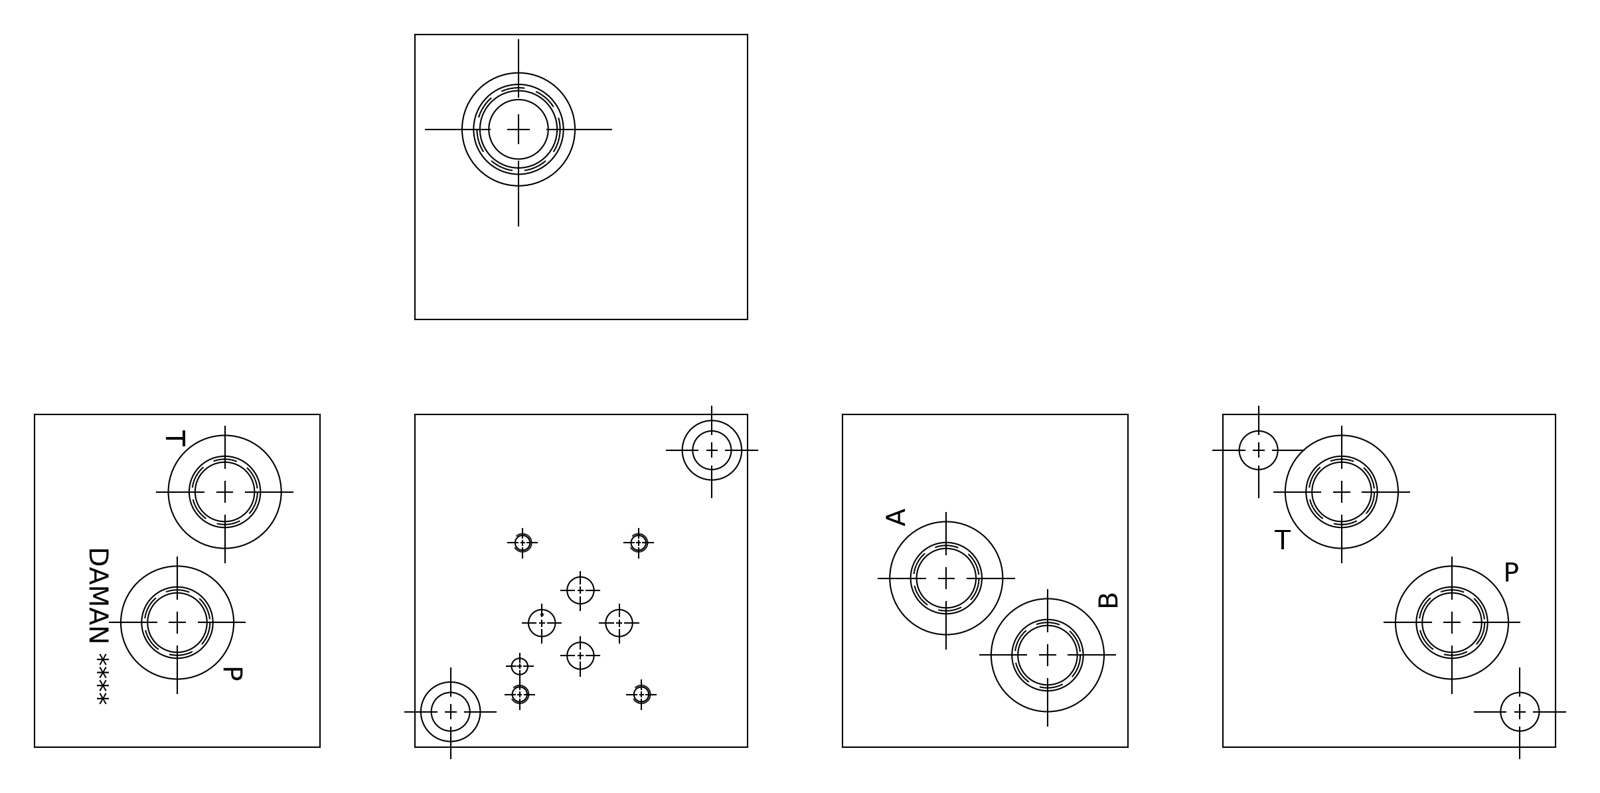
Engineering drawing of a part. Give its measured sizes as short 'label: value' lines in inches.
name: Part__D03SPRVC8S_3D
written by: Autodesk Inventor 2020 (AUTOMOTIVE_DESIGN)
unit: in
bodies: 1 solid, 564 faces (314 planar, 53 cylindrical, 197 other)
size: 3.5 × 3.5 × 3
volume: 31.87 in³; area: 94.45 in²
holes: 8× ⌀0.625, 6× ⌀0.689, 6× ⌀0.75, 6× ⌀0.758, 6× ⌀1.206, 4× ⌀0.149, 4× ⌀0.19, 4× ⌀0.281, 2× ⌀0.406, 1× ⌀0.156, 1× ⌀0.563, 1× ⌀0.626
face distances: 3.5, 3, 0.031, 3.469, 0.125, 2.875, 3.438, 0.562, 0.324, 3.176
hole spacings: 0.741, 0.758, 0.868, 1.321, 1.335, 1.594, 2.026, 0.25
